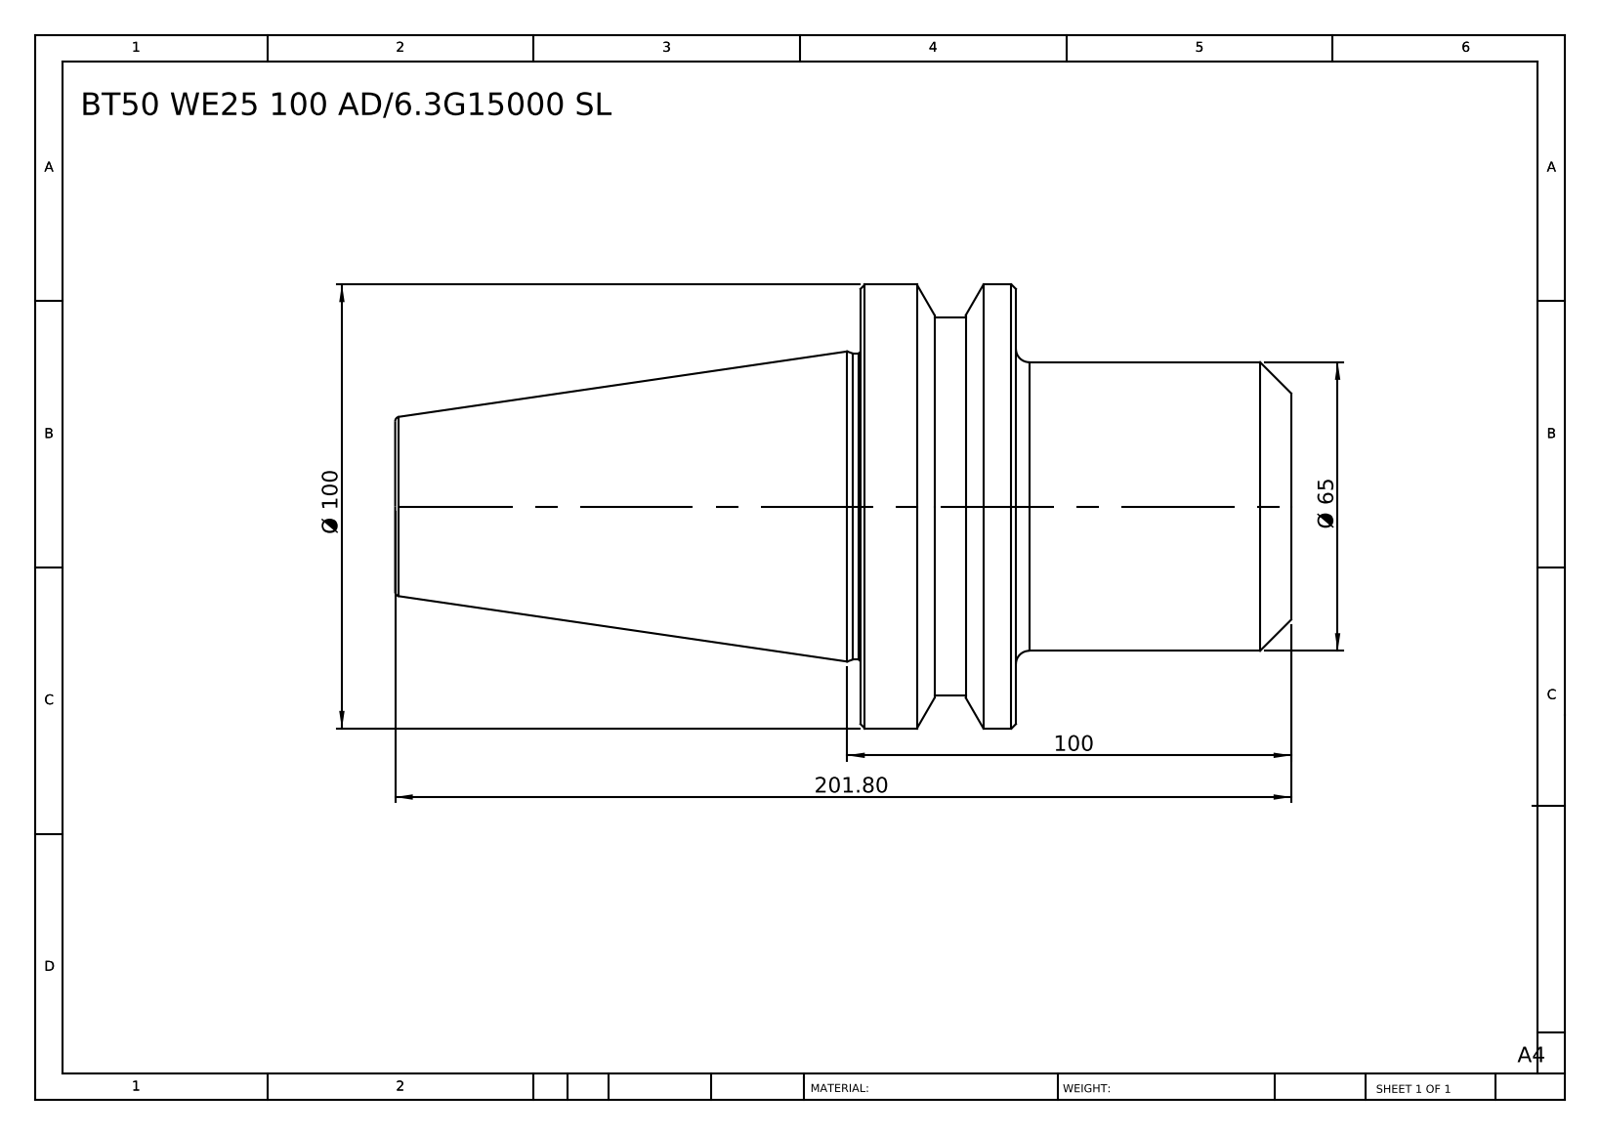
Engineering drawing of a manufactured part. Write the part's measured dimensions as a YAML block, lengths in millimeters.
part_name: "BT50 WE25 100 AD-6.3G15000 SL"
step_written_by: "SolidWorks 2014 (CONFIG_CONTROL_DESIGN)"
units: millimeters
bodies: {solids: 1, faces: 36, planar: 6, cylindrical: 10, other: 20}
overall_size: [201.8, 100, 100]
volume: 711553
surface_area: 55866
round_bosses_or_shafts:
  - {diameter: 100, count: 1}
  - {diameter: 85, count: 1}
  - {diameter: 69, count: 1}
  - {diameter: 65, count: 1}
face_to_face_distances: [35, 62, 97, 201.8, 139.8, 104.8, 73.3, 11.3, 23.7, 128.5]
